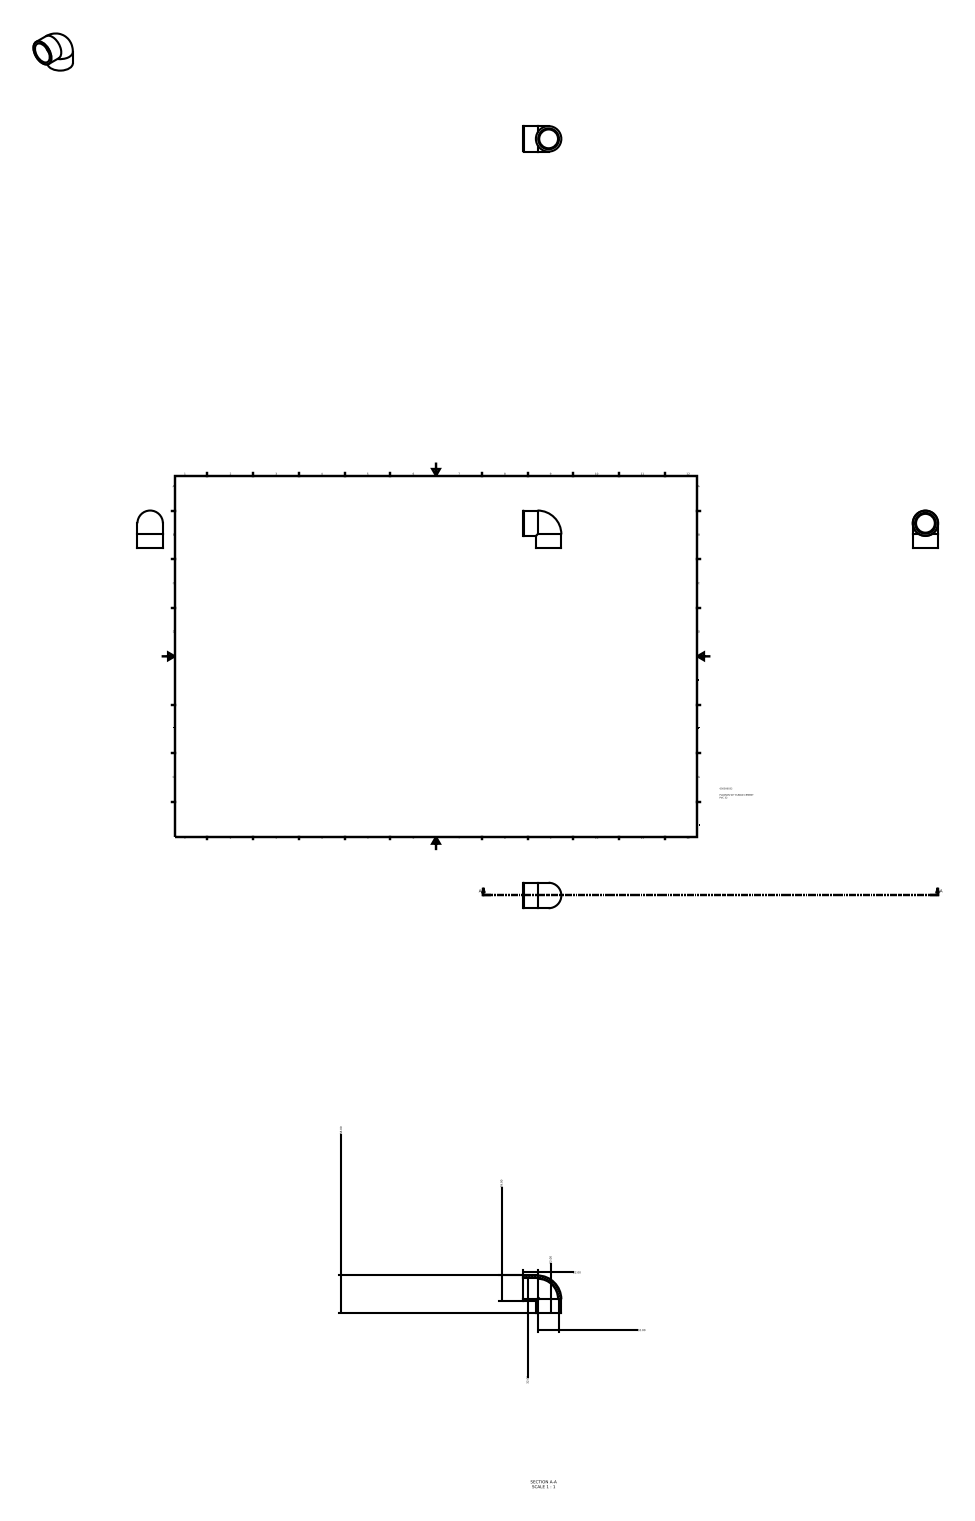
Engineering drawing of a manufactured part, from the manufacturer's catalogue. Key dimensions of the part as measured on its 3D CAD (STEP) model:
Part name (STEP PRODUCT): 050500032
STEP written by: Autodesk Inventor 2015 (AUTOMOTIVE_DESIGN)
Units: millimetres
Bodies: 1 solid, 11 faces (4 planar, 4 cylindrical, 3 other)
Overall size (bounding box): 58 × 58 × 39
Volume: 31 298 mm³ · Surface area: 16 370 mm²
Round holes (diameter × count): ⌀32 ×2
Round bosses / shafts (diameter × count): ⌀39 ×2
Main face-to-face distances: 22
